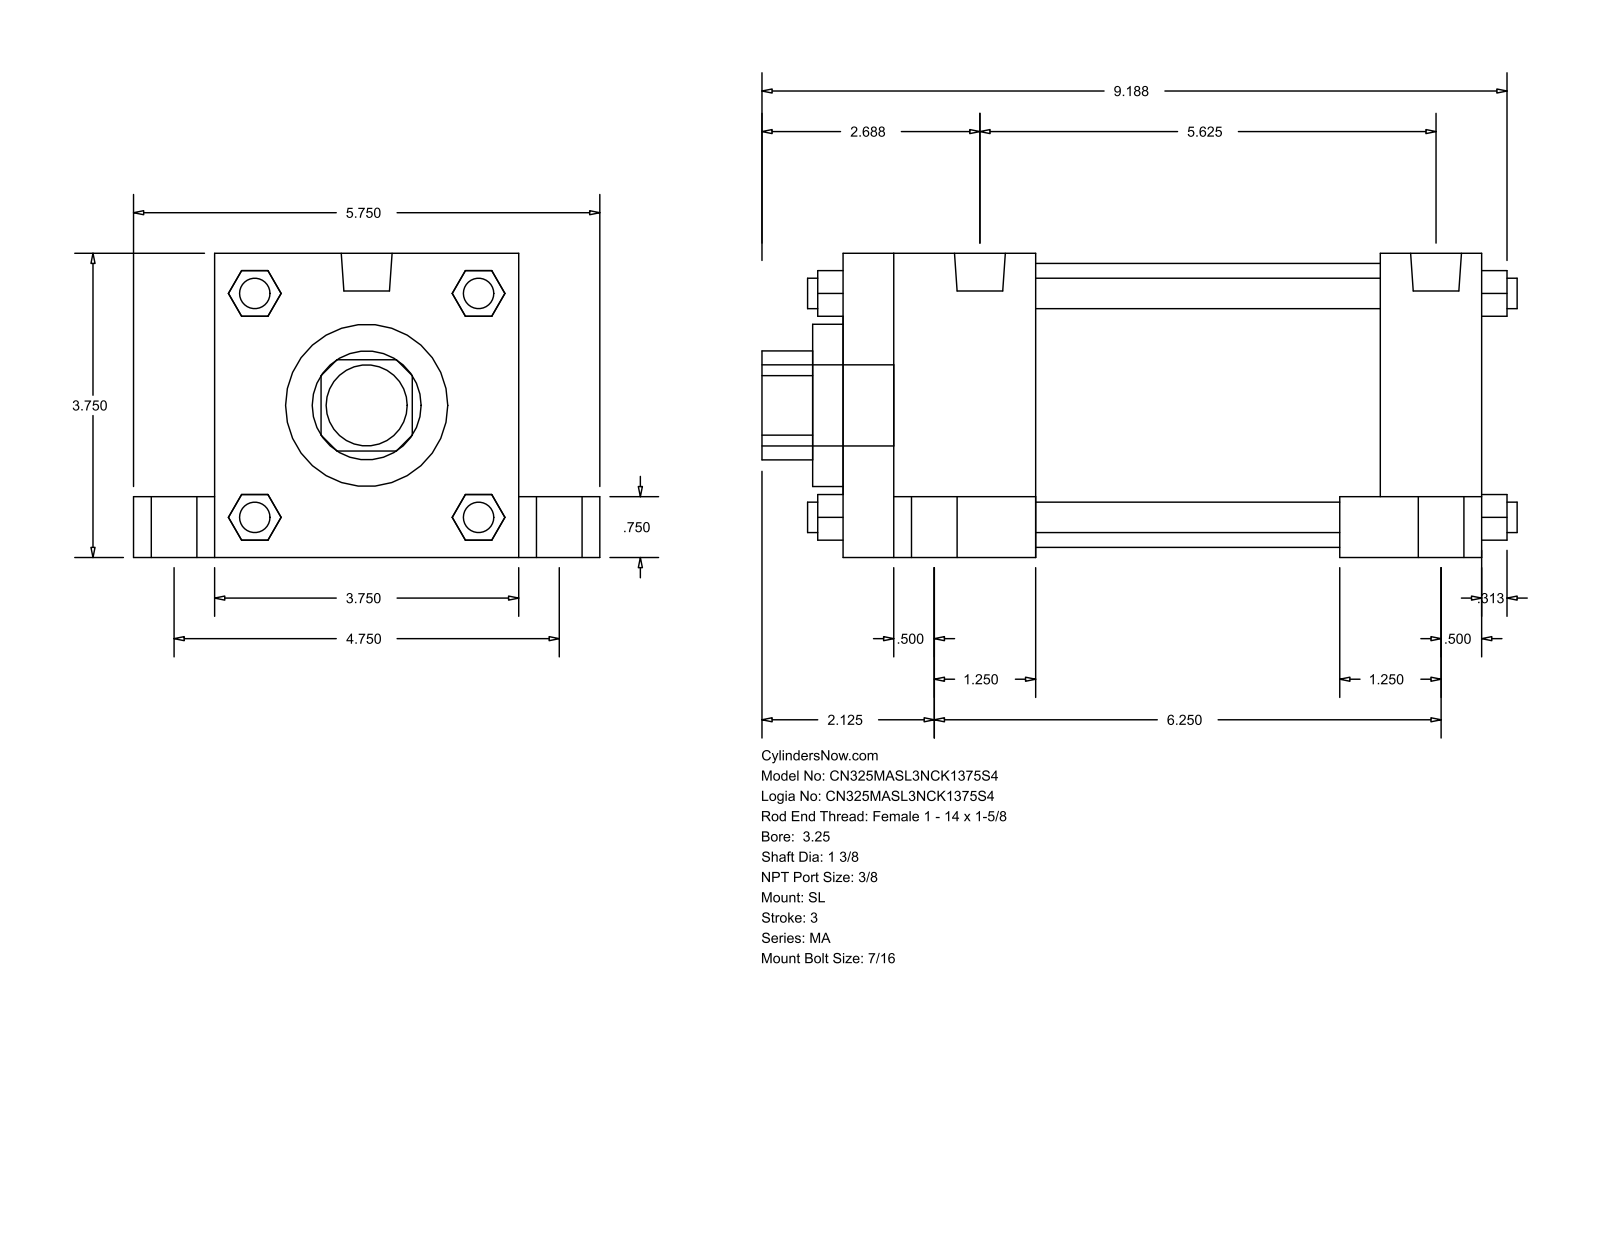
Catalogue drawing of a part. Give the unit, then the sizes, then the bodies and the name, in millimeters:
Units: millimetres
Overall size (bounding box): 236.54 × 146.05 × 95.25
Round holes (diameter × count): ⌀34.92 ×1, ⌀50.8 ×1, ⌀88.9 ×1
Round bosses / shafts (diameter × count): ⌀20.64 ×4, ⌀14.29 ×4, ⌀11.11 ×4, ⌀9.53 ×4, ⌀15.93 ×2, ⌀25.4 ×1
Partial cylindrical surfaces — rounded edges, fillets, slot ends (radius × count): R17.06 ×1
Main face-to-face distances: 95.24, 200.03, 25.41, 120.65, 168.28, 31.75, 60.32, 107.96, 139.71, 19.05
Bodies: 0 solids, 148 faces (112 planar, 36 cylindrical, 0 other)
Part name (STEP PRODUCT): MA_SL__0325_1.375
STEP written by: GSSL Pune (CONFIG_CONTROL_DESIGN)
